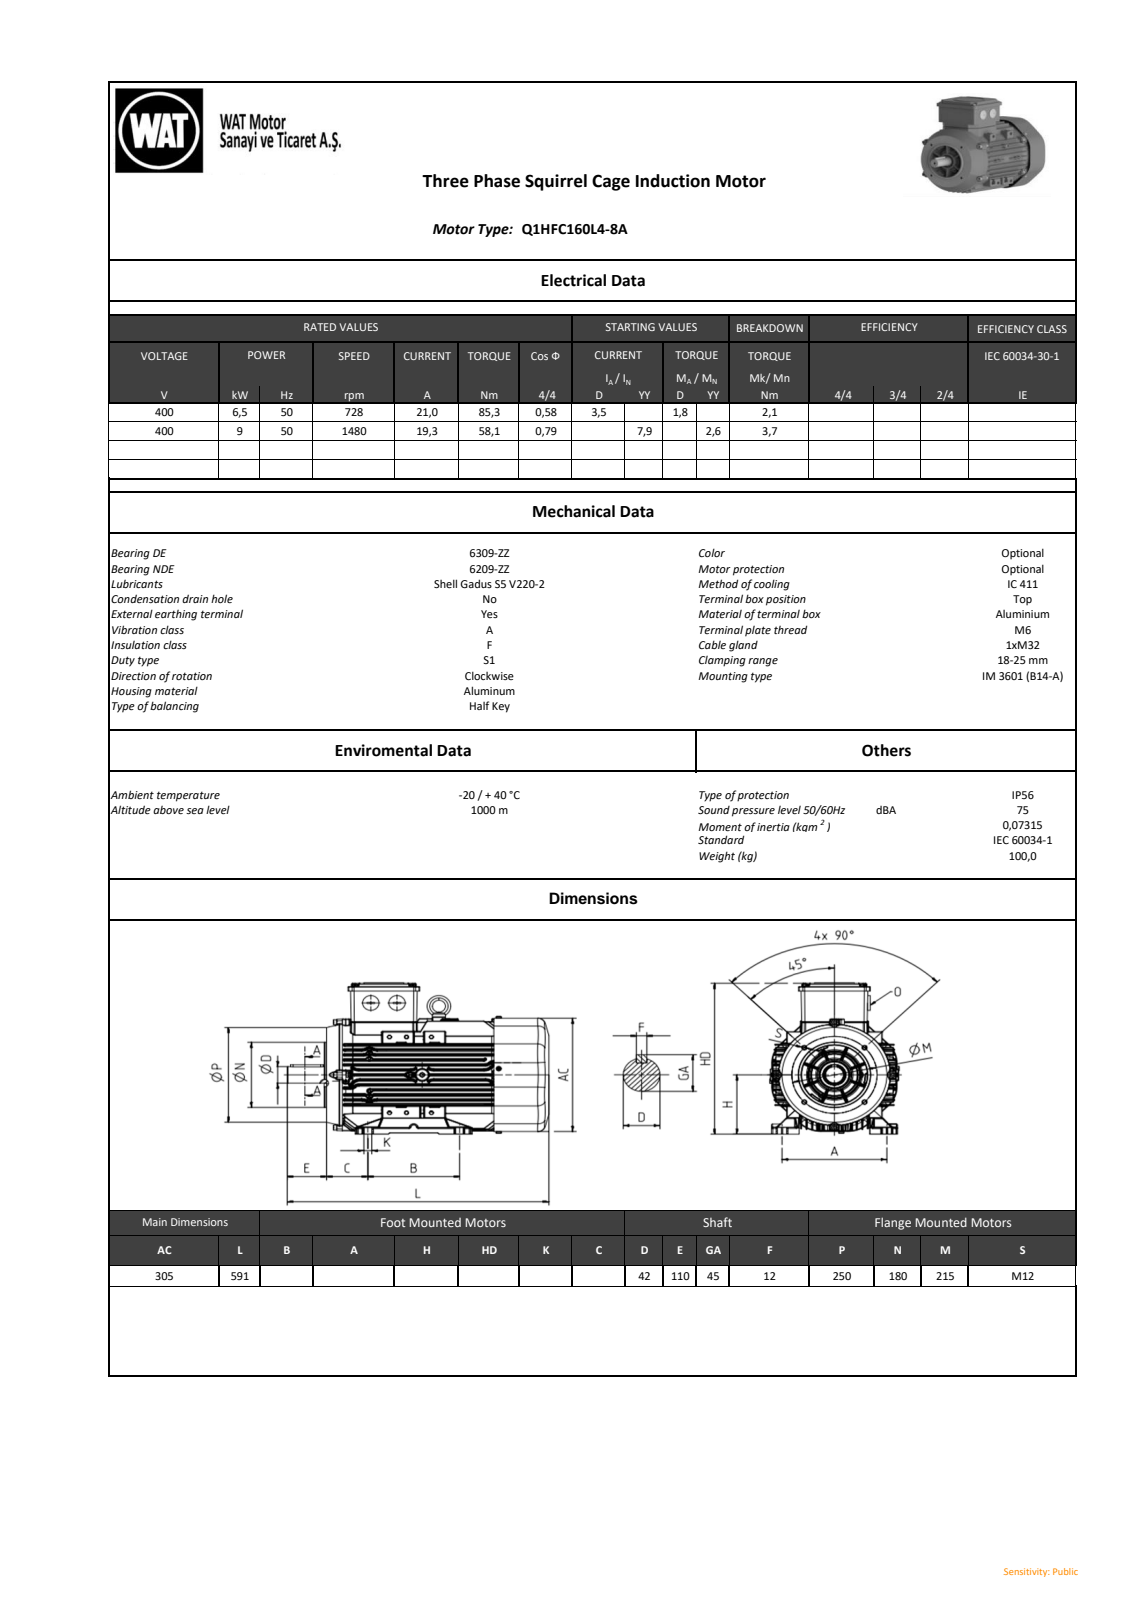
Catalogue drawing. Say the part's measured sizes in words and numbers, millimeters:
The part is named "DIS GORUNUS QH160 FC_stp_objects". Its 3-D file was written by "SIEMENS PLM Software NX2206.8101 (AP203_CONFIGURATION_CONTROLLED_3D_DESIGN_OF_MECHANICAL_PARTS_AND_ASSEMBLIES_MIM_LF)". It is 0 solids with 6547 faces: 1592 planar, 2852 cylindrical and 2103 other. Overall it measures 590.7 by 373.66 by 314 millimeters. Round holes: 4 of diameter 10.3, 4 of diameter 15, 2 of diameter 8, 1 of diameter 7, 1 of diameter 10, 1 of diameter 14, 1 of diameter 17, 1 of diameter 72, 1 of diameter 85.63, 1 of diameter 94, 1 of diameter 114, 1 of diameter 134. Round bosses or shafts: 4 of diameter 8, 2 of diameter 38, 2 of diameter 13, 1 of diameter 272.5, 1 of diameter 180, 1 of diameter 178, 1 of diameter 158, 1 of diameter 138. Partial cylindrical surfaces (rounded edges, fillets, slot ends): 738 of radius 0.5, 486 of radius 1, 95 of radius 2, 82 of radius 4, 66 of radius 2.5, 47 of radius 5, 34 of radius 3, 16 of radius 5.5. The main face-to-face distances are 144, 168, 11.92, 9.62, 14.77, 168.39, 24.39, 158.77, 120, 11.85. The hole center spacings are 100.99, 231.35, 142.5, 201.53, 107.49, 107.24, 107.47, 107.52.
